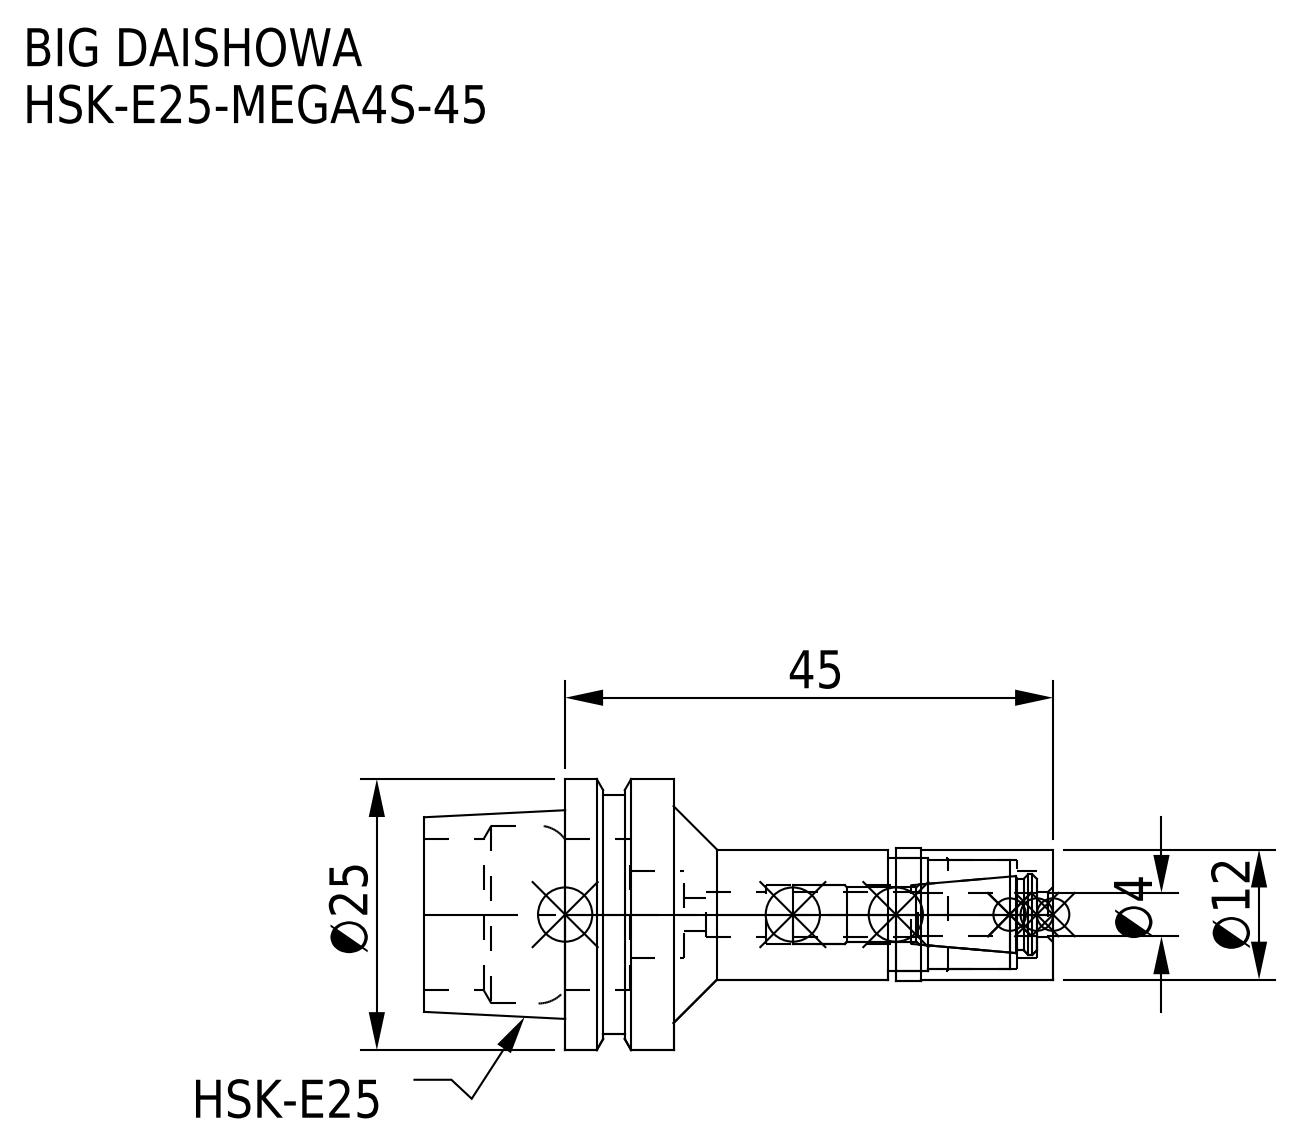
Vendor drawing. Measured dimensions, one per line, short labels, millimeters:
name: HSK-E25-MEGA4S-45_1.stp; HE25MS04045-040_ASM.stp; HSK-E25-MEGA4S-45-040-FreeParts; HSK-E25-MEGA4S-45-040.stp (+3 more)
written by: SolidWorks 2019 (CONFIG_CONTROL_DESIGN)
unit: mm
bodies: 2 solids, 74 faces (18 planar, 40 cylindrical, 16 other)
size: 58 × 25 × 25
volume: 8 109 mm³; area: 6 367 mm²
holes: 1× ⌀3, 1× ⌀4.1, 1× ⌀4.2, 1× ⌀5.4, 1× ⌀8, 1× ⌀10, 1× ⌀10.5, 1× ⌀14, 1× ⌀16.4
bosses: 1× ⌀25, 1× ⌀22, 1× ⌀12.3, 1× ⌀12
face distances: 10, 13, 4.05, 5.95, 23, 18.95, 35, 39.05, 45, 58
